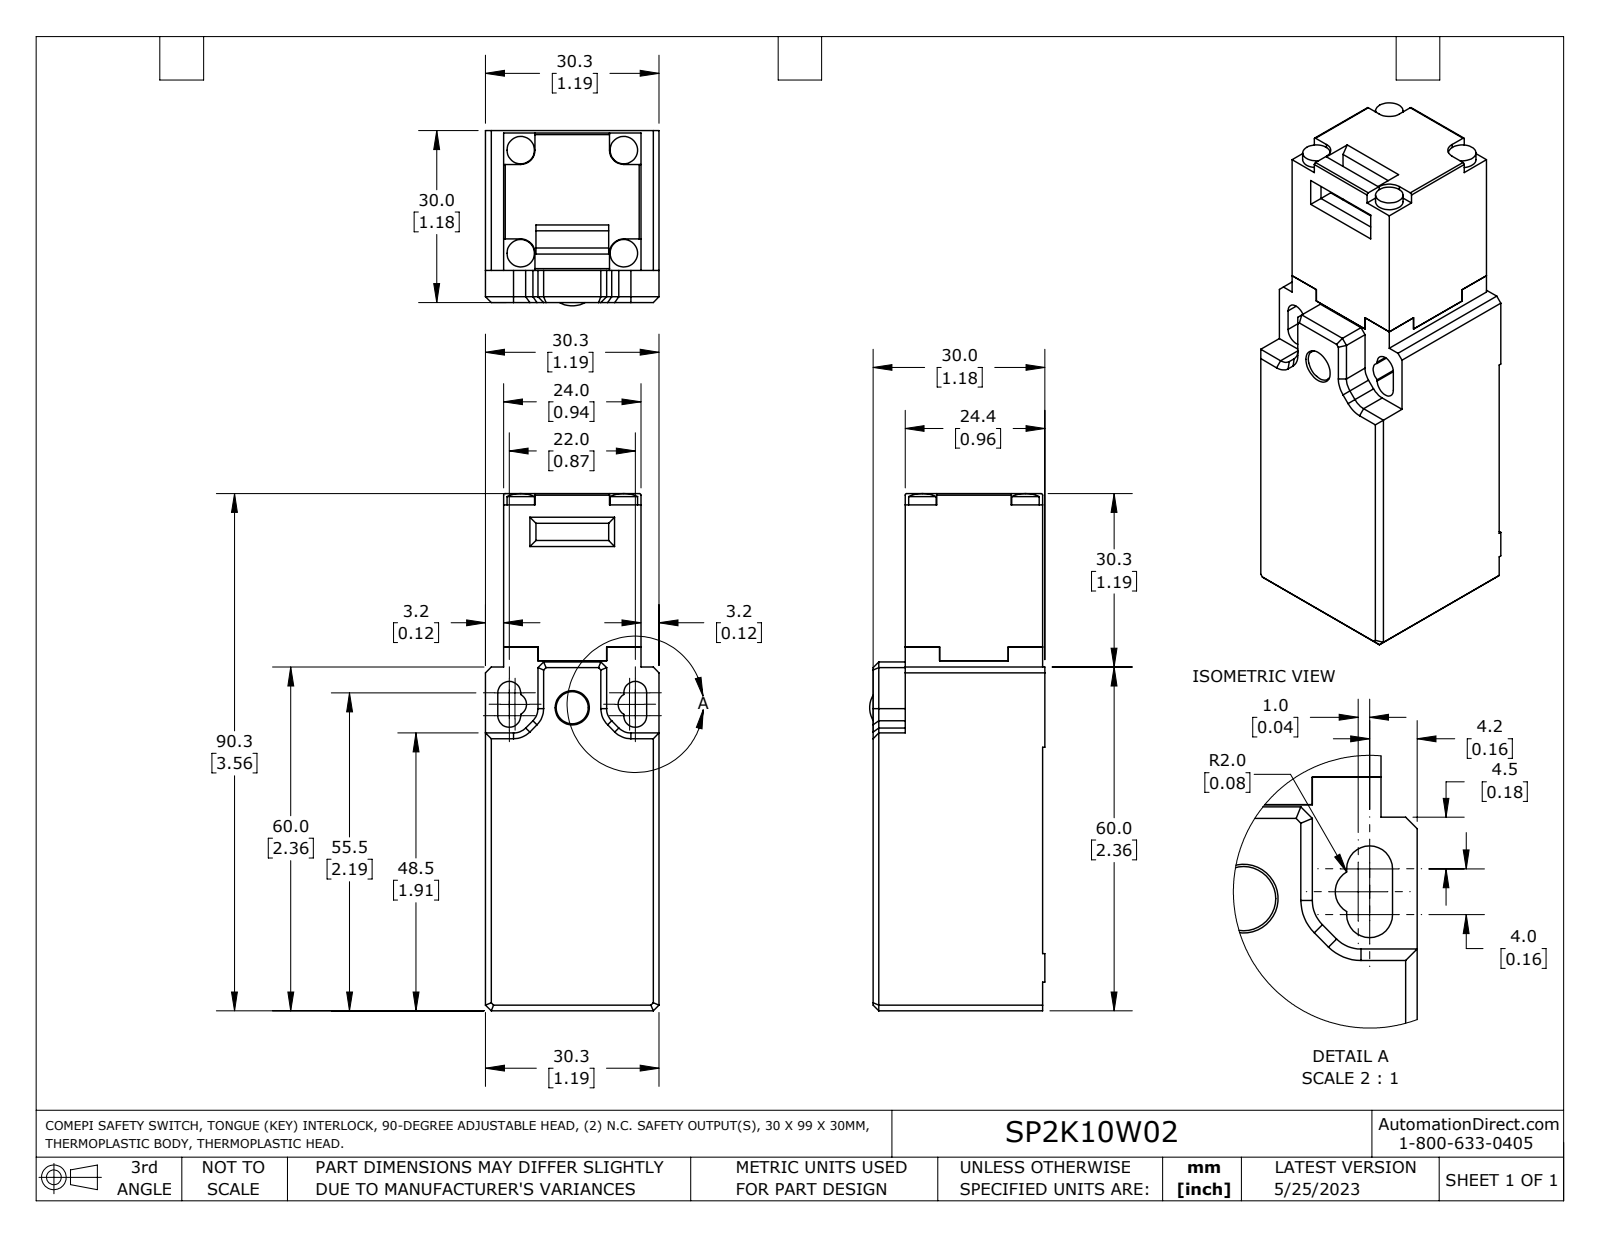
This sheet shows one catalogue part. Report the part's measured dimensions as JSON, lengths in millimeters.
{"part_name": "SP2K10W02", "step_written_by": "SolidWorks 2021 (AUTOMOTIVE_DESIGN)", "units": "millimeters", "bodies": {"solids": 2, "faces": 156, "planar": 112, "cylindrical": 34, "other": 10}, "overall_size": [90.3, 30.6, 30.3], "volume_mm3": 65560, "surface_area_mm2": 15680, "round_holes": [[6, 1], [17, 1], [19, 1]], "round_bosses_or_shafts": [[4.8, 4], [5.6, 1]], "partial_cylinders_radius": [[2, 6], [0.3, 4], [2.5, 4], [3, 4], [10, 1], [10.2, 1]], "face_to_face_distances": [30.3, 24, 29.6, 3.1, 27.2, 5.6, 61.1, 0.4, 24.4, 30]}
